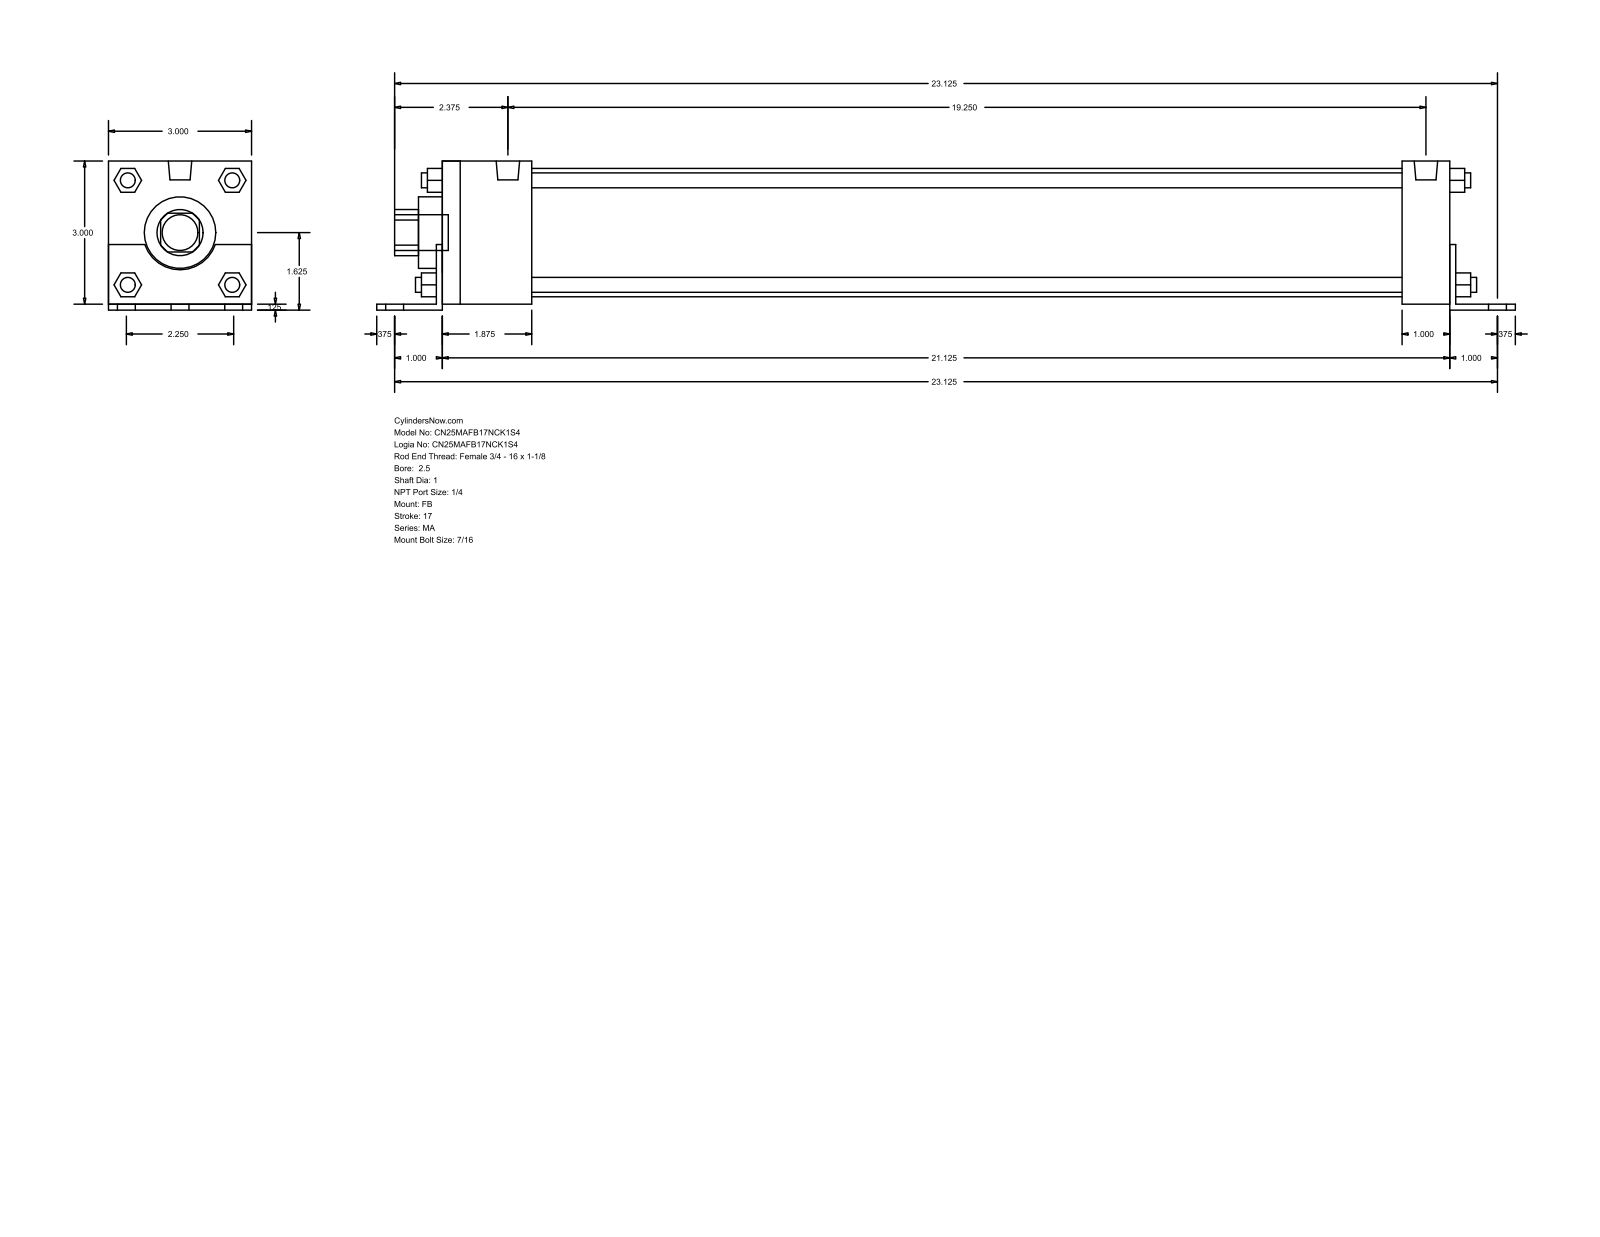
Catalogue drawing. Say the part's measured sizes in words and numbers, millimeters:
The part is named "MA_FB__0250_1". Its 3-D file was written by "GSSL Pune (CONFIG_CONTROL_DESIGN)". It is 0 solids with 140 faces: 105 planar, 35 cylindrical and 0 other. Overall it measures 606.42 by 79.38 by 76.2 millimeters. Round holes: 1 of diameter 25.4, 1 of diameter 38.1, 1 of diameter 68.33. Round bosses or shafts: 8 of diameter 7.94, 6 of diameter 11.11, 2 of diameter 12.49, 1 of diameter 19.05. Partial cylindrical surfaces (rounded edges, fillets, slot ends): 1 of radius 12.29, 1 of radius 19.81. The main face-to-face distances are 76.2, 3.17, 79.37, 539.75, 536.58, 12.7, 25.4, 28.57, 47.63, 488.95.
